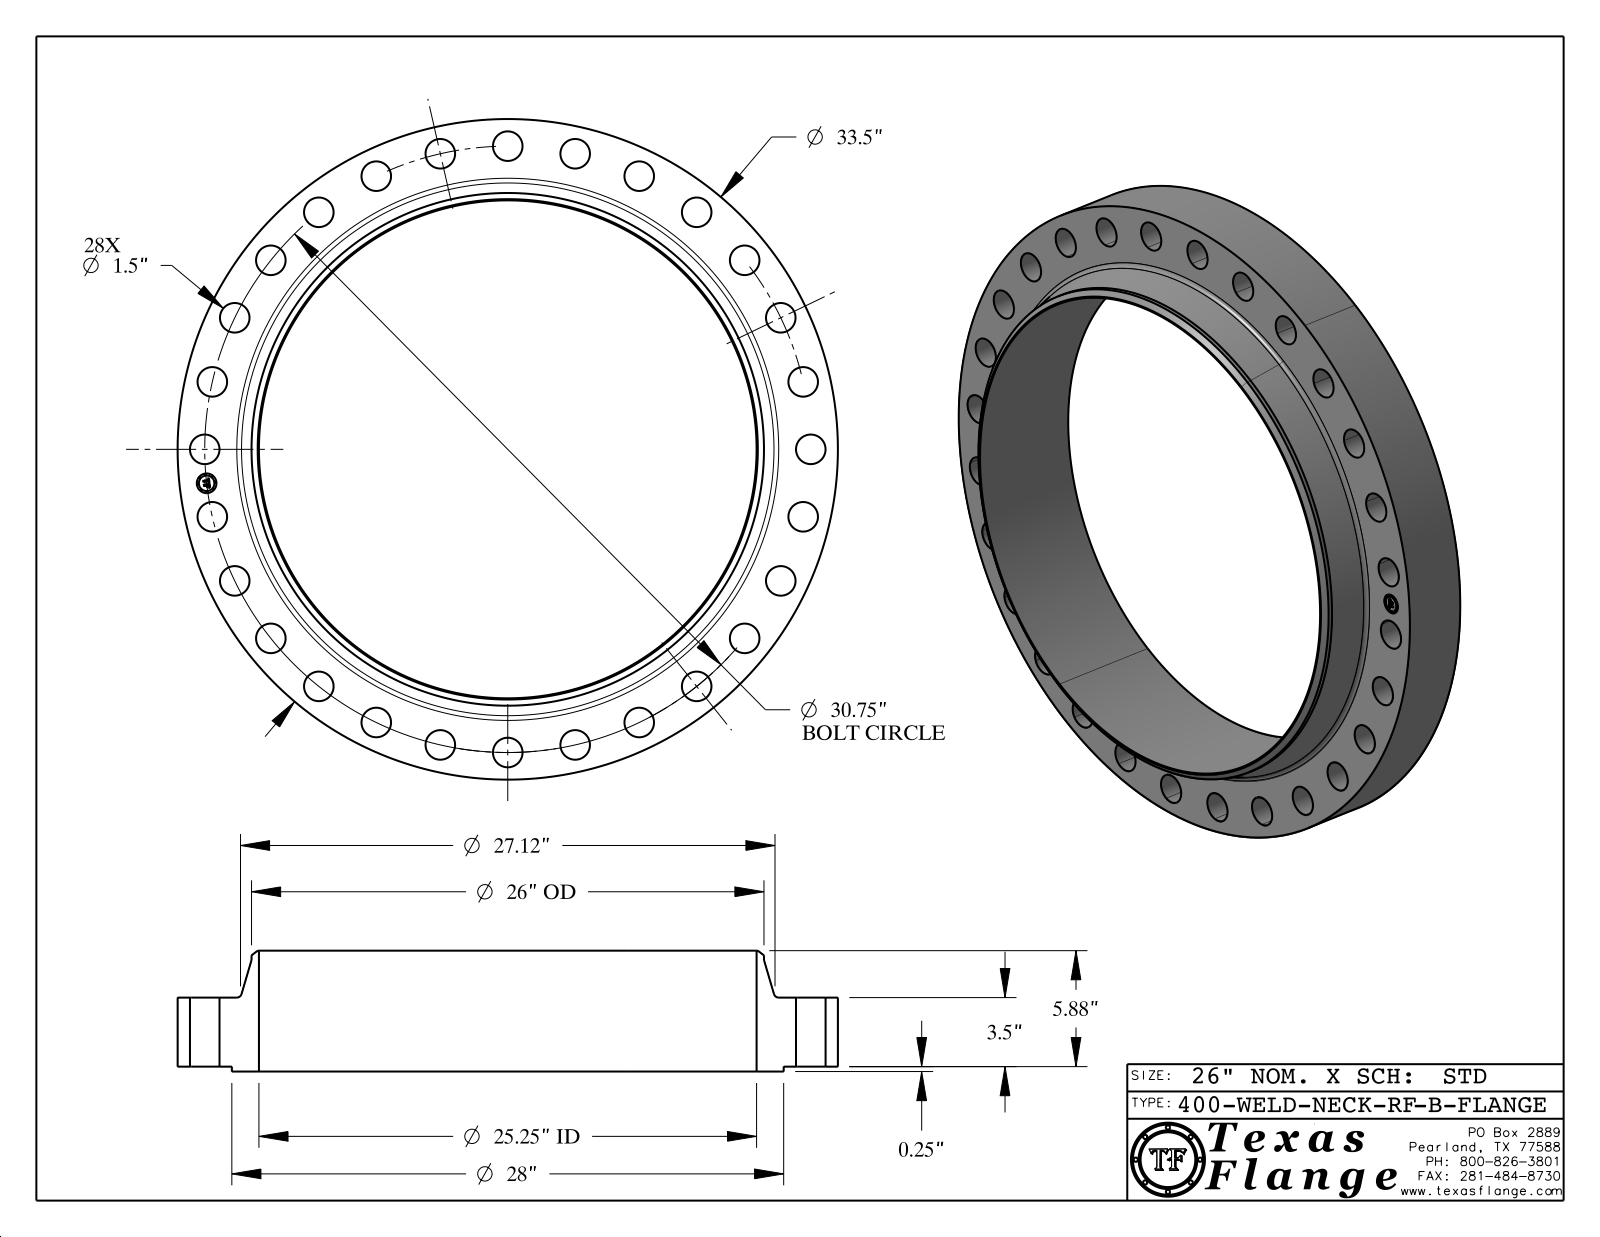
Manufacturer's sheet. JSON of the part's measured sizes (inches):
{"part_name": "400-WELD-NECK-RF, Series B", "step_written_by": "CATIA V5 STEP AP214 (AUTOMOTIVE_DESIGN)", "units": "inches", "bodies": {"solids": 1, "faces": 459, "planar": 369, "cylindrical": 84, "other": 6}, "overall_size": [33.5, 33.5, 6.13], "volume_in3": 1301, "surface_area_in2": 2141, "round_holes": [[1.5, 28], [1, 1], [25.25, 1]], "round_bosses_or_shafts": [[0.061, 8], [33.5, 1], [28, 1], [26, 1], [0.788, 1]], "face_to_face_distances": [3.5, 0.25, 3.75, 6.13, 5.88, 2.38, 3.735, 3.485, 0.015, 2.395], "hole_center_spacings": [6.843, 29.024, 15.375, 21.743, 13.342, 16.36, 19.172, 26.037]}
